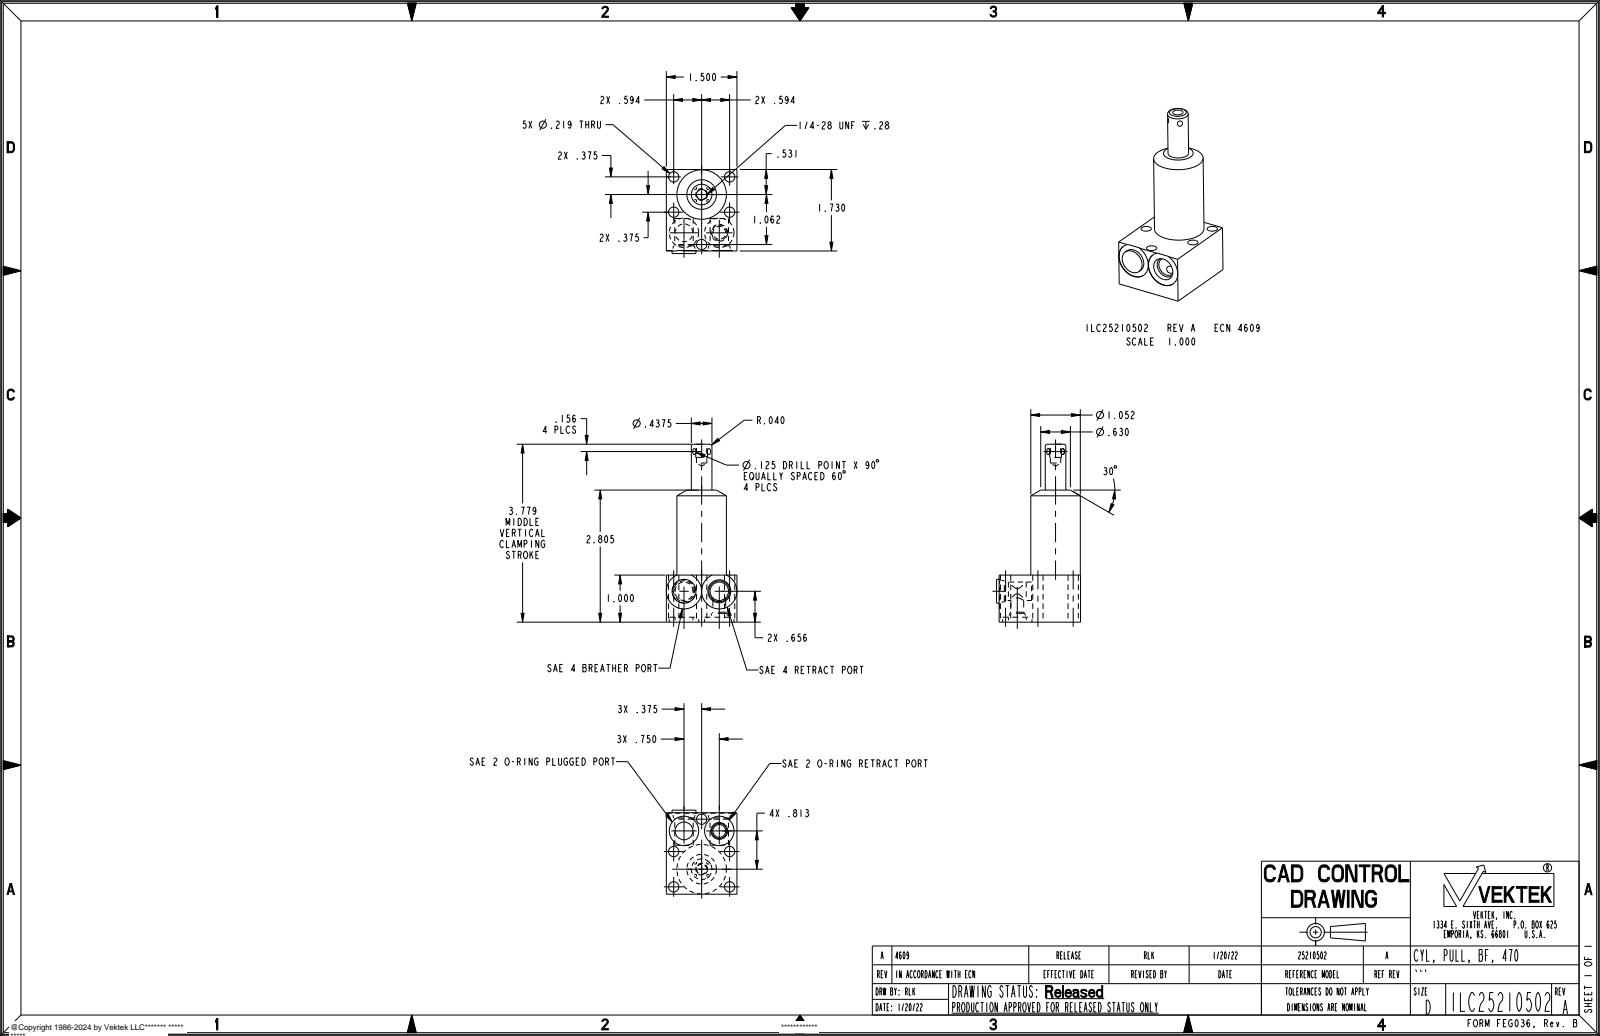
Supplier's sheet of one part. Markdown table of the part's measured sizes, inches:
| quantity | value |
| --- | --- |
| part name | ILC25210502 |
| STEP written by | CREO PARAMETRIC BY PTC INC, 2021164 (AUTOMOTIVE_DESIGN) |
| units | inches |
| bodies | 1 solid, 83 faces (21 planar, 36 cylindrical, 26 other) |
| overall size | 3.779 × 1.98 × 1.7 |
| volume | 3.858 in³ |
| surface area | 25.13 in² |
| round holes (diameter × count) | 0.219 × 5, 0.392 × 2, 0.625 × 2, 0.75 × 2, 0.221 × 1, 0.272 × 1 |
| round bosses / shafts (diameter × count) | 1.052 × 1, 0.507 × 1, 0.437 × 1, 0.378 × 1, 0.25 × 1 |
| main face-to-face distances | 1.5, 1, 1.72, 1.73, 0.105, 0.895, 0.69, 0.68, 1.04, 0.055 |
| hole center spacings | 0.702, 0.75, 0.45, 0.49, 0.895, 0.908, 1.063, 1.188 |
